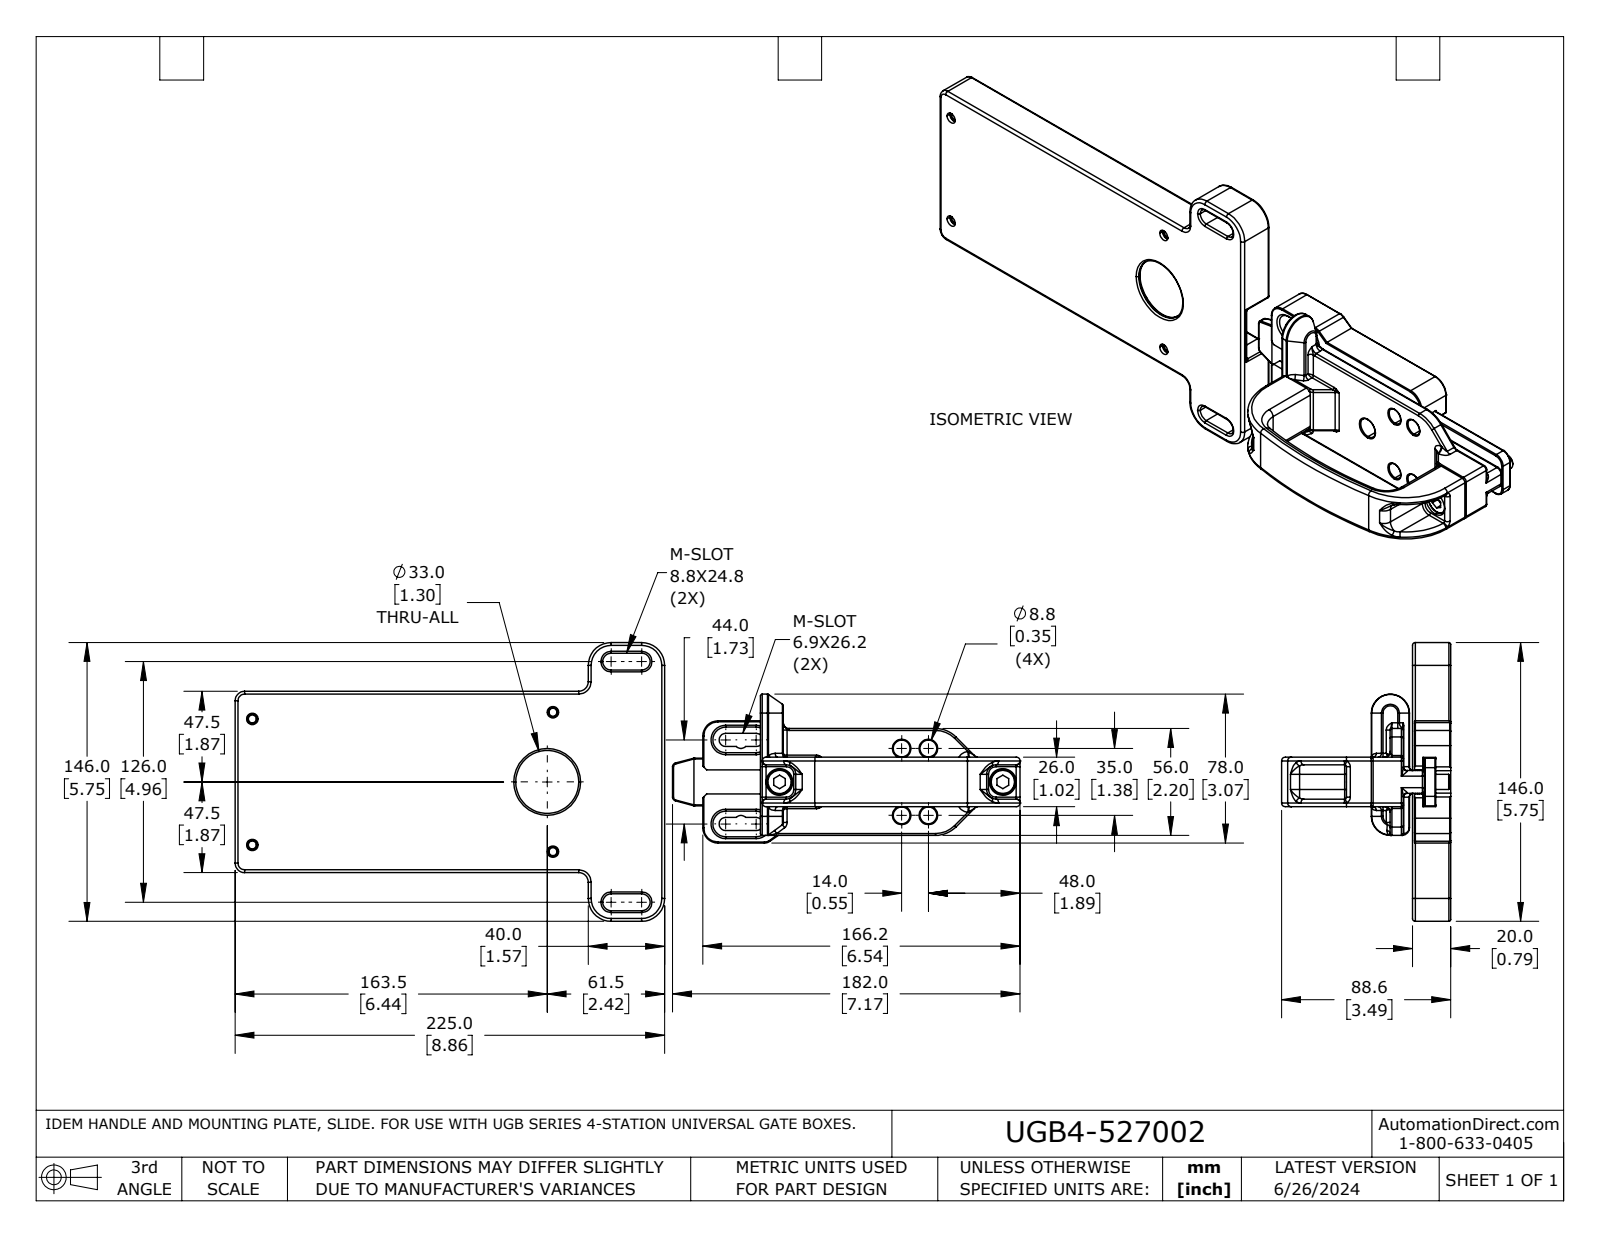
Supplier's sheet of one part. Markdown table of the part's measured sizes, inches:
| quantity | value |
| --- | --- |
| part name | 527002 UGB4-SFH-M |
| STEP written by | SolidWorks 2021 (CONFIG_CONTROL_DESIGN) |
| units | inches |
| bodies | 9 solids, 1125 faces (246 planar, 505 cylindrical, 374 other) |
| overall size | 16.189 × 5.748 × 3.488 |
| volume | 21.29 in³ |
| surface area | 249.1 in² |
| round holes (diameter × count) | 0.165 × 6, 0.346 × 6, 0.197 × 4, 0.236 × 4, 0.266 × 2, 0.551 × 2, 0.354 × 1, 0.433 × 1, 1.299 × 1 |
| round bosses / shafts (diameter × count) | 0.512 × 2, 0.354 × 2, 0.315 × 2, 0.197 × 2 |
| partial cylindrical surfaces (radius × count) | 0.039 × 98, 0.02 × 60, 0.079 × 50, 0.118 × 22, 0.197 × 20, 0.059 × 7, 0.136 × 6, 0.173 × 4 |
| main face-to-face distances | 0.098, 0.689, 0.787, 0.276, 0.48, 0.748, 0.244, 0.118, 0.307, 0.382 |
| hole center spacings | 0.406, 4.816, 0.551, 0.709, 1.046, 1.378, 1.442, 1.484 |
